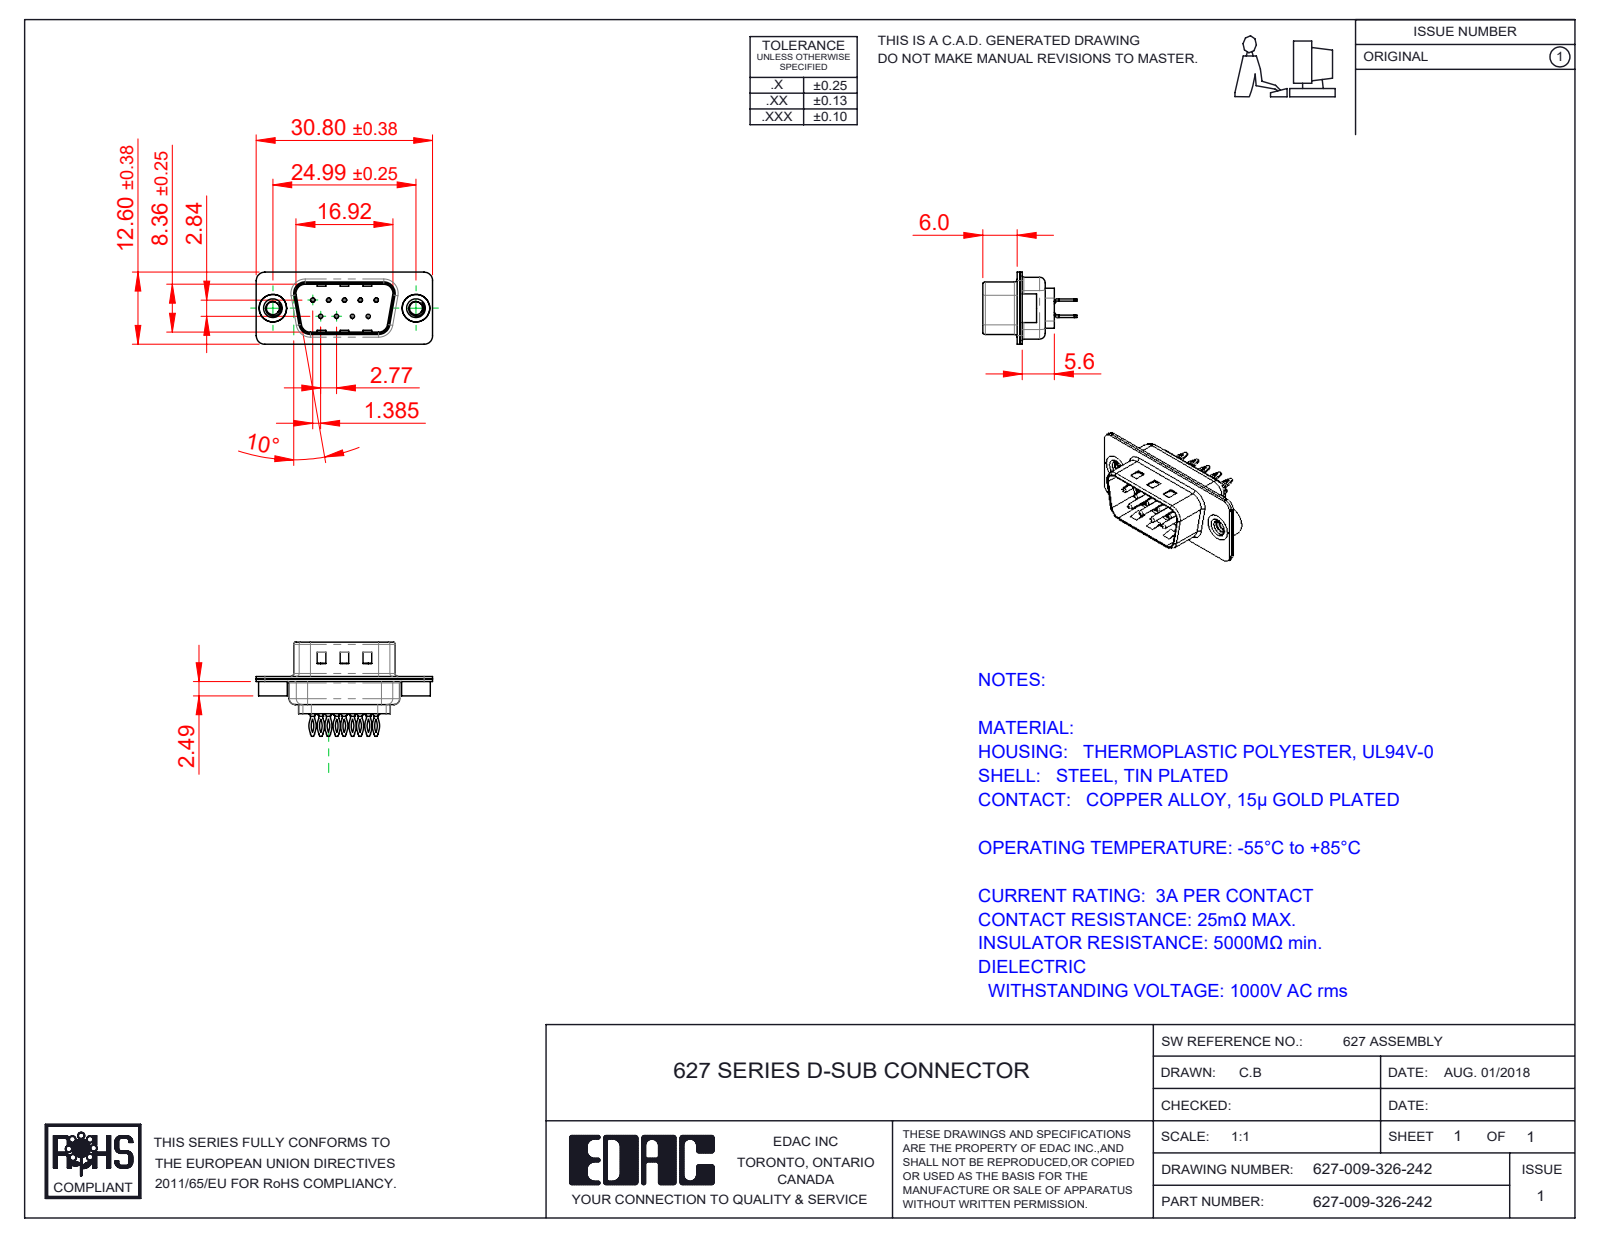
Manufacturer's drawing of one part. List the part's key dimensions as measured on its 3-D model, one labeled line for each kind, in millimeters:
Part name (STEP PRODUCT): 627 Shell Front_09 Contacts; 627 Contact Row 1_26L; 627 4-40 Threaded Rivet; 627 Shell Rear_09 Contacts (+3 more)
STEP written by: SolidWorks 2020 (CONFIG_CONTROL_DESIGN)
Units: millimetres
Bodies: 14 solids, 984 faces (287 planar, 406 cylindrical, 291 other)
Overall size (bounding box): 30.8 × 16.45 × 12.6
Volume: 1 307 mm³ · Surface area: 3 895 mm²
Round holes (diameter × count): ⌀0.35 ×9, ⌀1.1 ×9, ⌀1.6 ×9, ⌀2.26 ×2, ⌀4 ×2, ⌀4.8 ×2
Round bosses / shafts (diameter × count): ⌀2 ×9, ⌀1.5 ×9, ⌀0.75 ×9, ⌀5 ×2, ⌀4.9 ×2
Partial cylindrical surfaces — rounded edges, fillets, slot ends (radius × count): R1.5 ×18, R2.92 ×18, R3.33 ×18, R2 ×12, R0.5 ×8, R1.6 ×8, R0.25 ×4, R0.6 ×4
Main face-to-face distances: 0.4, 0.45, 0.9, 0.82, 9.58, 1.4, 8.76, 0.5, 1.5, 6.05
Hole centre spacings: 3.16, 2.77, 5.54, 5.03, 5.04, 8.31, 7.48, 7.49
